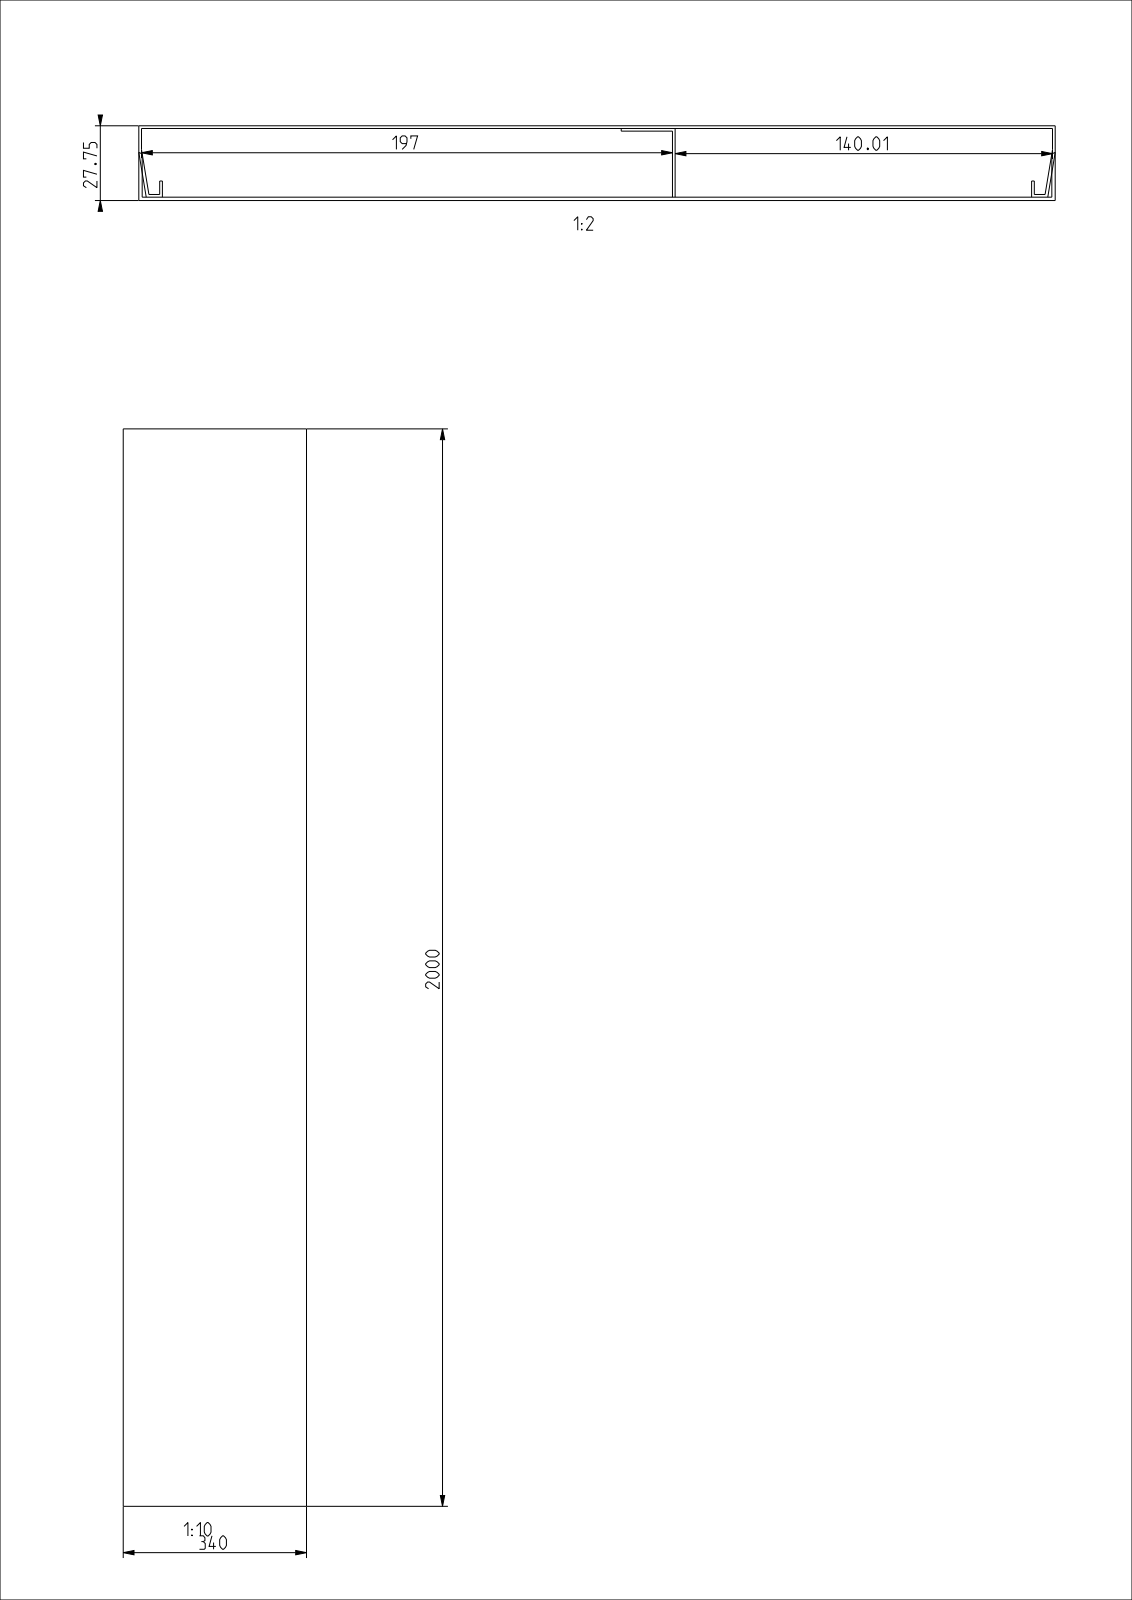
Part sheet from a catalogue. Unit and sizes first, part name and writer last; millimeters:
Units: millimetres
Overall size (bounding box): 2000 × 340 × 47.75
Main face-to-face distances: 1, 1.25, 46.5, 47.75, 45.5, 46.75, 0.99, 339, 340, 198.99
Volume: 1 960 000 mm³ · Surface area: 3 489 000 mm²
Bodies: 2 solids, 39 faces (39 planar, 0 cylindrical, 0 other)
Part name (STEP PRODUCT): UK340482KUN_OBERTEIL; UK340482KUN_UNTERTEIL; UK340482KUN_ASM
STEP written by: CREO PARAMETRIC BY PTC INC, 2022024 (AUTOMOTIVE_DESIGN)
